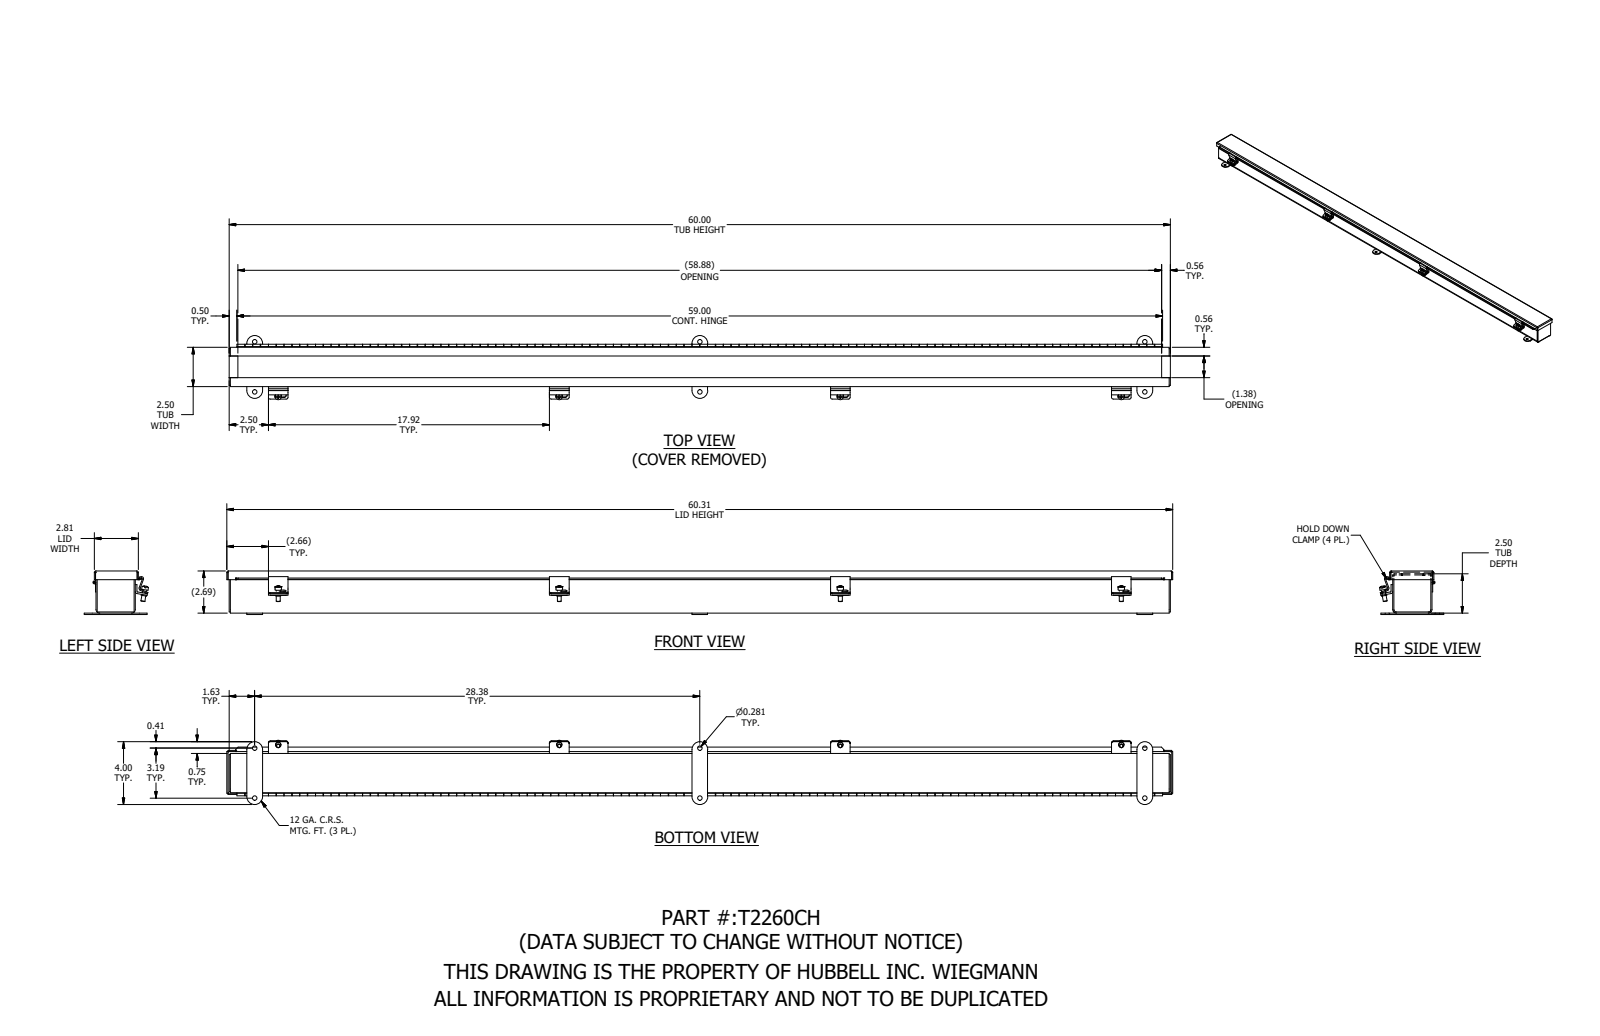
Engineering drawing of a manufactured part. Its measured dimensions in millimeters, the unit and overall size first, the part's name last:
Units: millimetres
Overall size (bounding box): 1532 × 104 × 70.7
Round holes (diameter × count): ⌀7.1 ×6, ⌀5 ×4, ⌀2.9 ×1
Round bosses / shafts (diameter × count): ⌀10.4 ×4, ⌀8.7 ×4, ⌀6.4 ×4, ⌀5.1 ×1, ⌀2.5 ×1
Partial cylindrical surfaces — rounded edges, fillets, slot ends (radius × count): R3.2 ×16, R0.8 ×9, R2.7 ×9, R3.4 ×8, R12.7 ×6, R1.6 ×3, R3.2 ×3, R4 ×2
Main face-to-face distances: 1.9, 61.6, 66.4, 63.5, 59.7, 68.3, 64.5, 64.6, 2.9, 4.8
Hole centre spacings: 80.9, 455.1, 720.7, 720.7, 725.2, 725.3, 1441.5, 1443.7
Volume: 999 800 mm³ · Surface area: 1 134 000 mm²
Bodies: 22 solids, 1221 faces (592 planar, 601 cylindrical, 28 other)
Part name (STEP PRODUCT): T2260CH
STEP written by: SolidWorks 2021 (AUTOMOTIVE_DESIGN)
